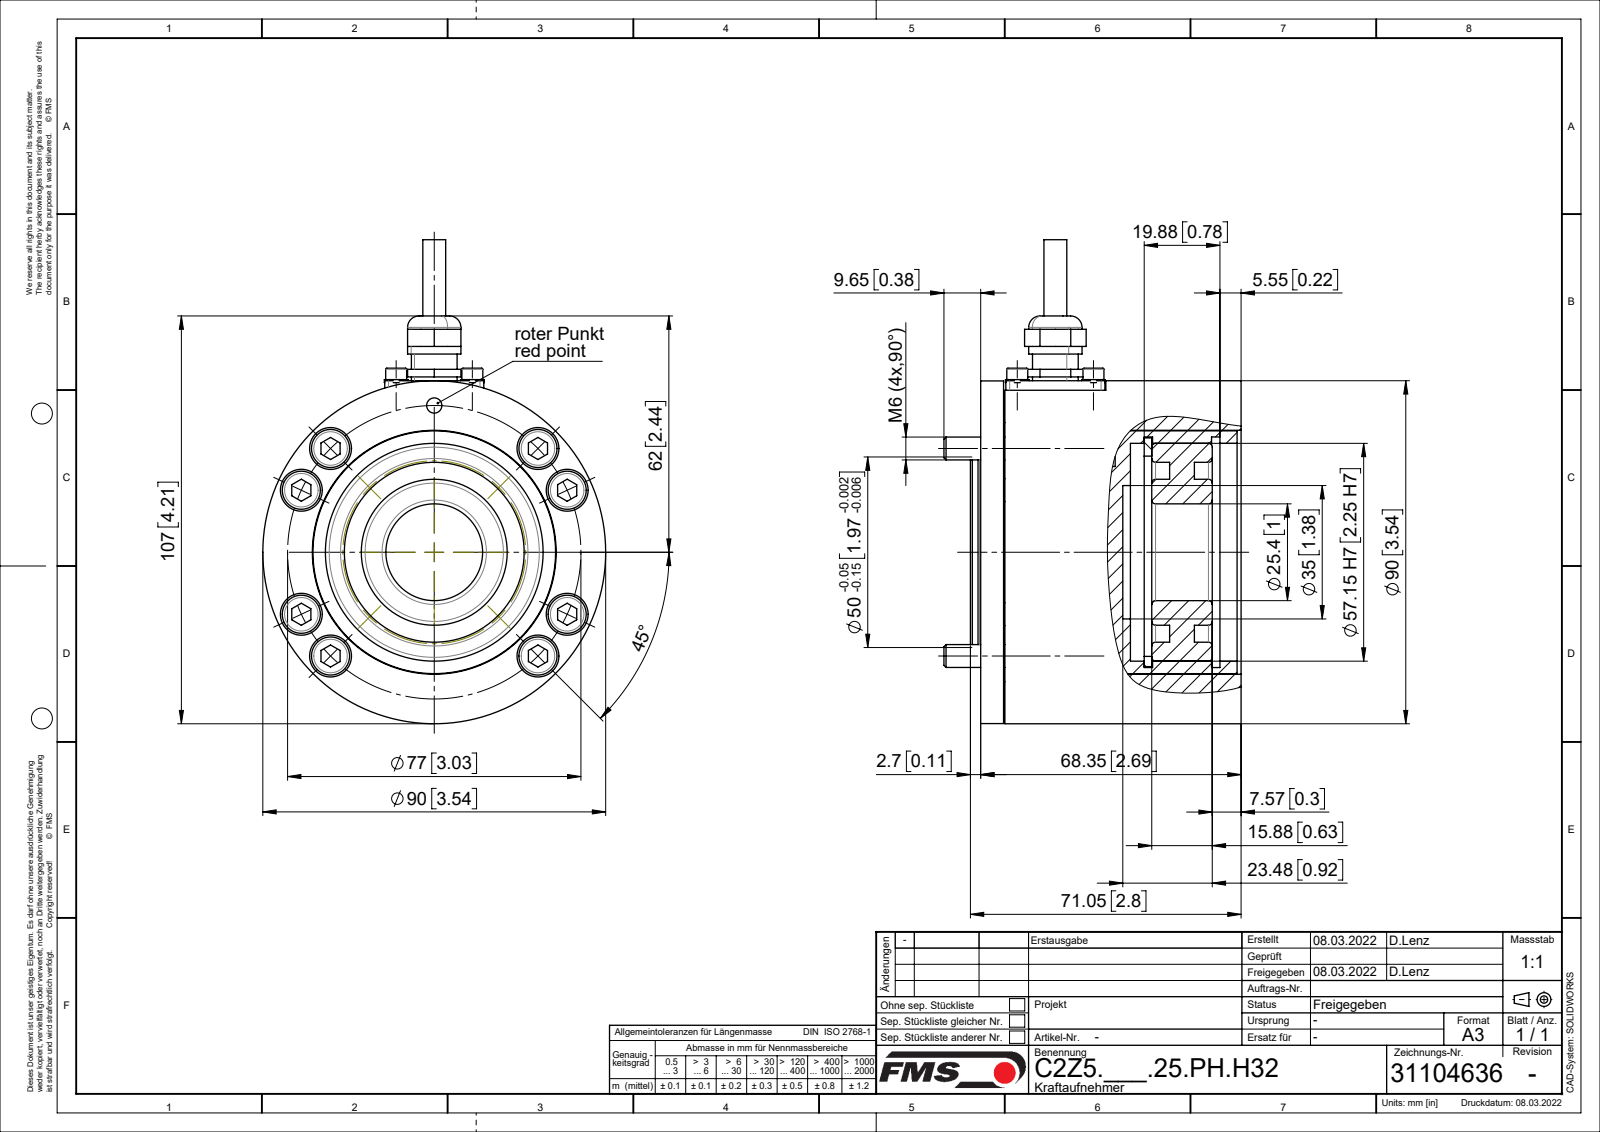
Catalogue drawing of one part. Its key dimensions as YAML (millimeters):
part_name: "Federringe_DIN127A_M03; PKL_NLJ1_vereinfacht_01; Zyl-Schr DIN912_M6x30; 31104636 (+8 more)"
step_written_by: "SolidWorks 2018 (CONFIG_CONTROL_DESIGN)"
units: millimeters
bodies: {solids: 24, faces: 556, planar: 222, cylindrical: 232, other: 102}
overall_size: [127, 90, 78]
volume: 296468
surface_area: 118599
round_holes:
  - {diameter: 6.5, count: 8}
  - {diameter: 11, count: 8}
  - {diameter: 2.5, count: 6}
  - {diameter: 3.1, count: 4}
  - {diameter: 3.4, count: 4}
  - {diameter: 5, count: 4}
  - {diameter: 7, count: 4}
  - {diameter: 4, count: 2}
  - {diameter: 6, count: 1}
  - {diameter: 10.2, count: 1}
  - {diameter: 12.2, count: 1}
  - {diameter: 18, count: 1}
round_bosses_or_shafts:
  - {diameter: 10, count: 8}
  - {diameter: 6, count: 8}
  - {diameter: 6.2, count: 4}
  - {diameter: 5.5, count: 4}
  - {diameter: 3, count: 4}
  - {diameter: 90, count: 1}
  - {diameter: 89.9, count: 1}
  - {diameter: 63.7, count: 1}
partial_cylinders:
  - {radius: 0.1, count: 4}
  - {radius: 1, count: 4}
  - {radius: 4.16, count: 2}
  - {radius: 5, count: 2}
  - {radius: 23.2, count: 1}
  - {radius: 26.29, count: 1}
face_to_face_distances: [6, 3.3, 2.7, 33.05, 32, 38, 30, 29.3, 35.3, 28.95]
hole_center_spacings: [20, 38.5, 13.37, 14.14, 38.49, 44.16, 54.44, 63.07]
